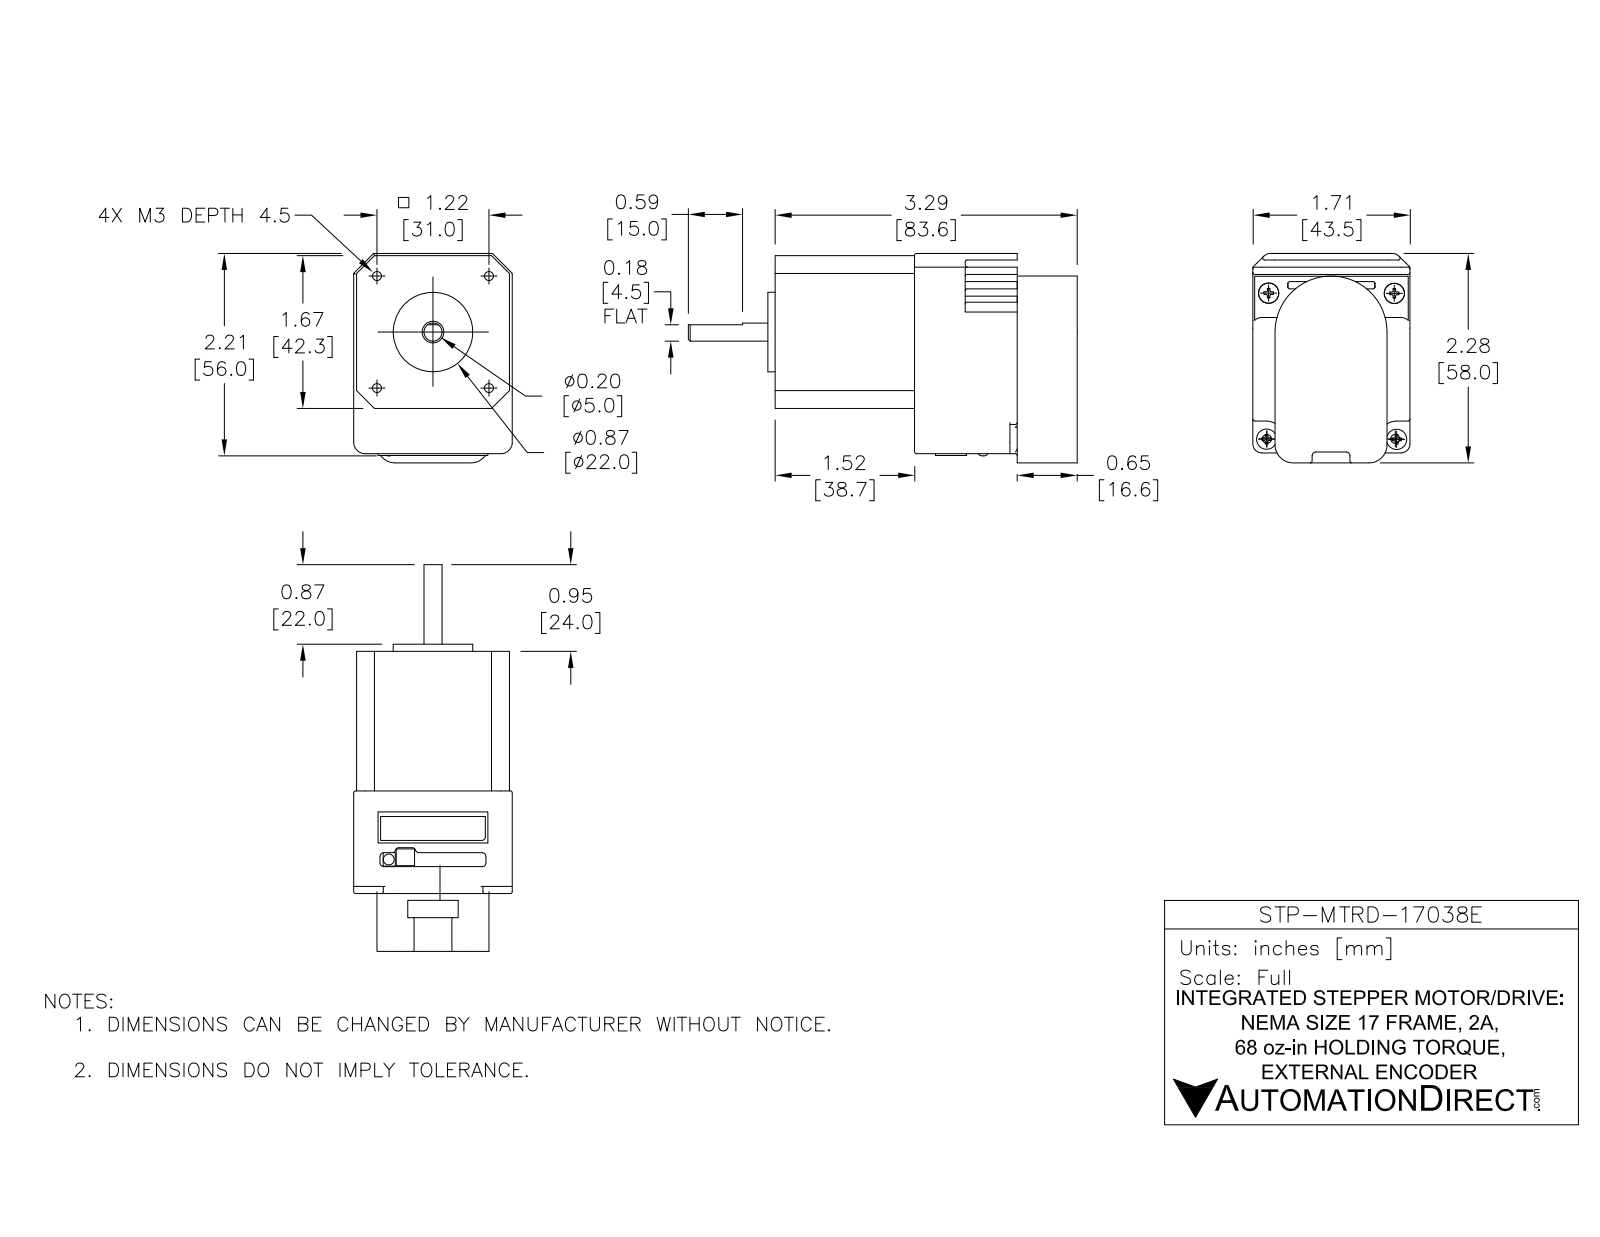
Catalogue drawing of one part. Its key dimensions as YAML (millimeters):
part_name: "STP-MTRD-17038E"
step_written_by: "SolidWorks 2017 (AUTOMOTIVE_DESIGN)"
units: millimeters
bodies: {solids: 1, faces: 485, planar: 192, cylindrical: 190, other: 103}
overall_size: [107.6, 57.95, 43.9]
volume: 147618
surface_area: 24062
round_holes:
  - {diameter: 2.5, count: 6}
  - {diameter: 1.98, count: 2}
  - {diameter: 3, count: 2}
  - {diameter: 7.5, count: 1}
  - {diameter: 15, count: 1}
round_bosses_or_shafts:
  - {diameter: 6, count: 2}
  - {diameter: 5.6, count: 2}
  - {diameter: 22, count: 1}
  - {diameter: 5, count: 1}
  - {diameter: 3, count: 1}
partial_cylinders:
  - {radius: 0.5, count: 85}
  - {radius: 1, count: 8}
  - {radius: 2.5, count: 8}
  - {radius: 10.96, count: 6}
  - {radius: 0.68, count: 4}
  - {radius: 25.37, count: 4}
  - {radius: 0.68, count: 2}
  - {radius: 3, count: 2}
face_to_face_distances: [2, 41.9, 39.9, 4, 83.59, 43.9, 6, 6.45, 37.45, 4.45]
hole_center_spacings: [16.61, 21.92, 29.44, 31, 7.95, 9.53, 9.61, 14.24]
